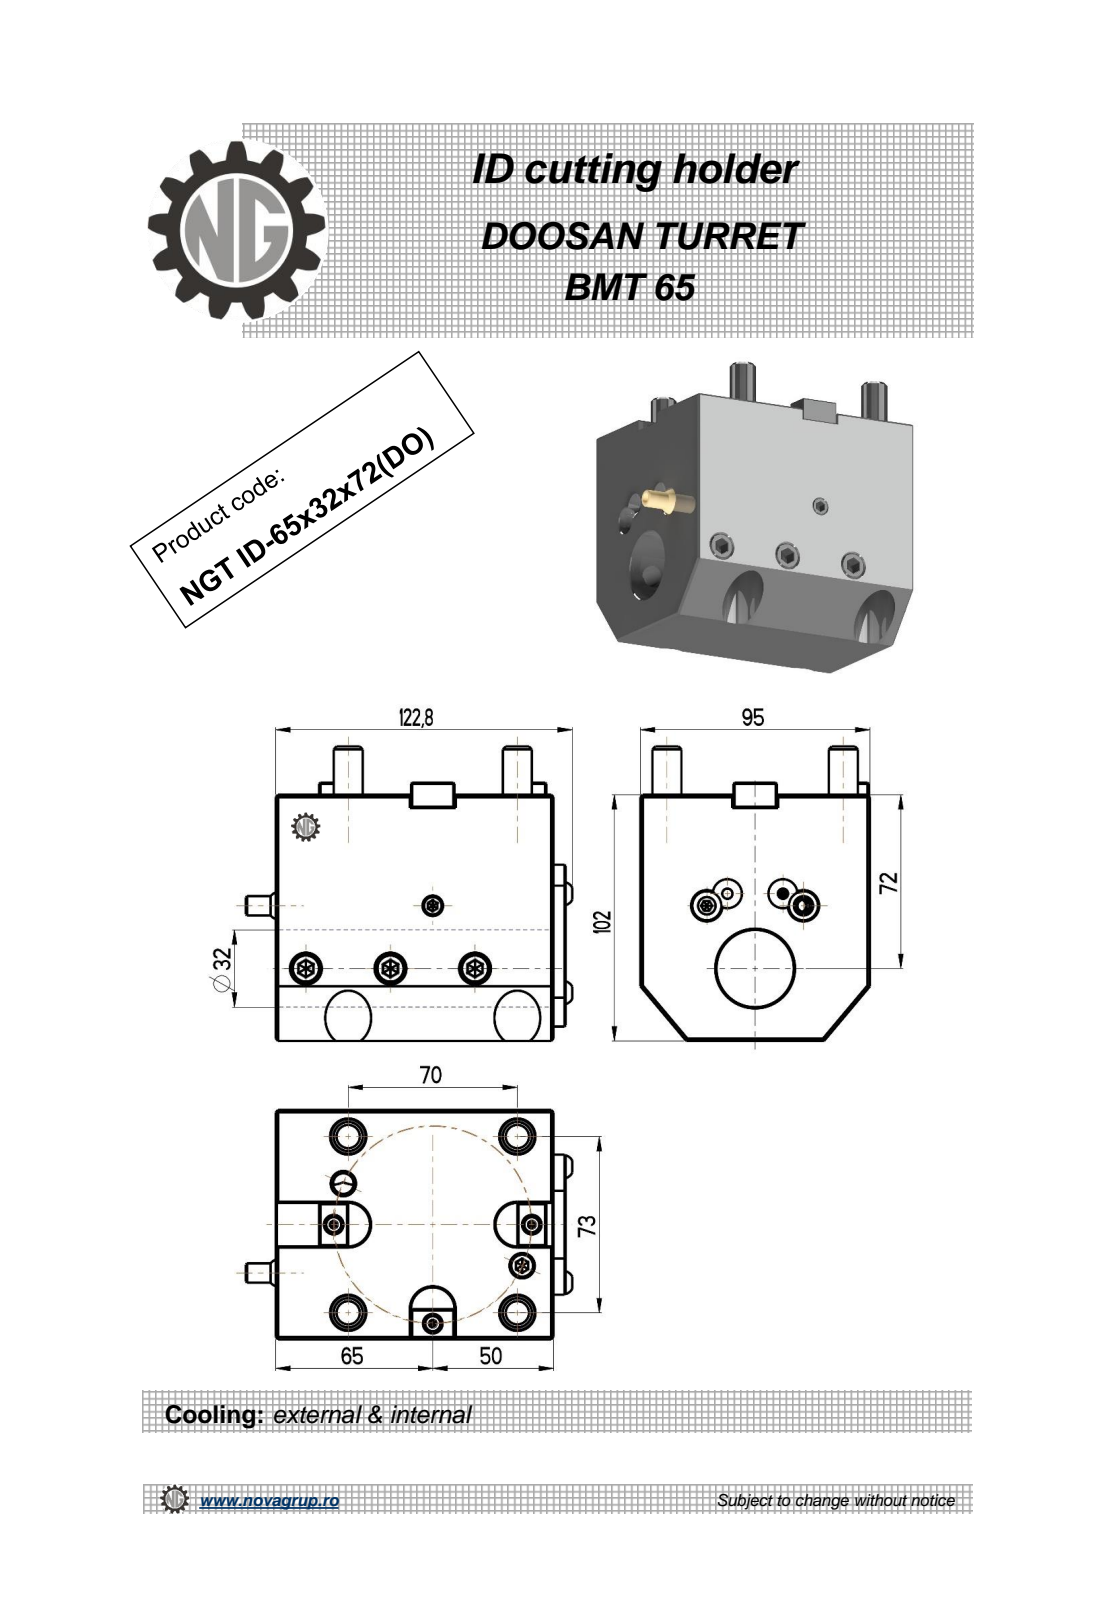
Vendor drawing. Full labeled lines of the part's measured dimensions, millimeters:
Part name (STEP PRODUCT): NGT_ID_65_32_72_DO
STEP written by: PRO/ENGINEER BY PARAMETRIC TECHNOLOGY CORPORATION, 2010280 (CONFIG_CONTROL_DESIGN)
Units: millimetres
Bodies: 1 solid, 373 faces (203 planar, 73 cylindrical, 97 other)
Overall size (bounding box): 135.09 × 122 × 95
Volume: 987 452 mm³ · Surface area: 83 840 mm²
Round holes (diameter × count): ⌀10.2 ×3, ⌀5 ×1, ⌀8.5 ×1, ⌀32 ×1
Round bosses / shafts (diameter × count): ⌀12 ×4, ⌀8 ×1
Partial cylindrical surfaces — rounded edges, fillets, slot ends (radius × count): R0.61 ×36, R0.51 ×6, R9 ×3
Main face-to-face distances: 95, 102, 115, 5, 120, 97, 20, 38, 18, 107
Hole centre spacings: 35, 32.8, 70
